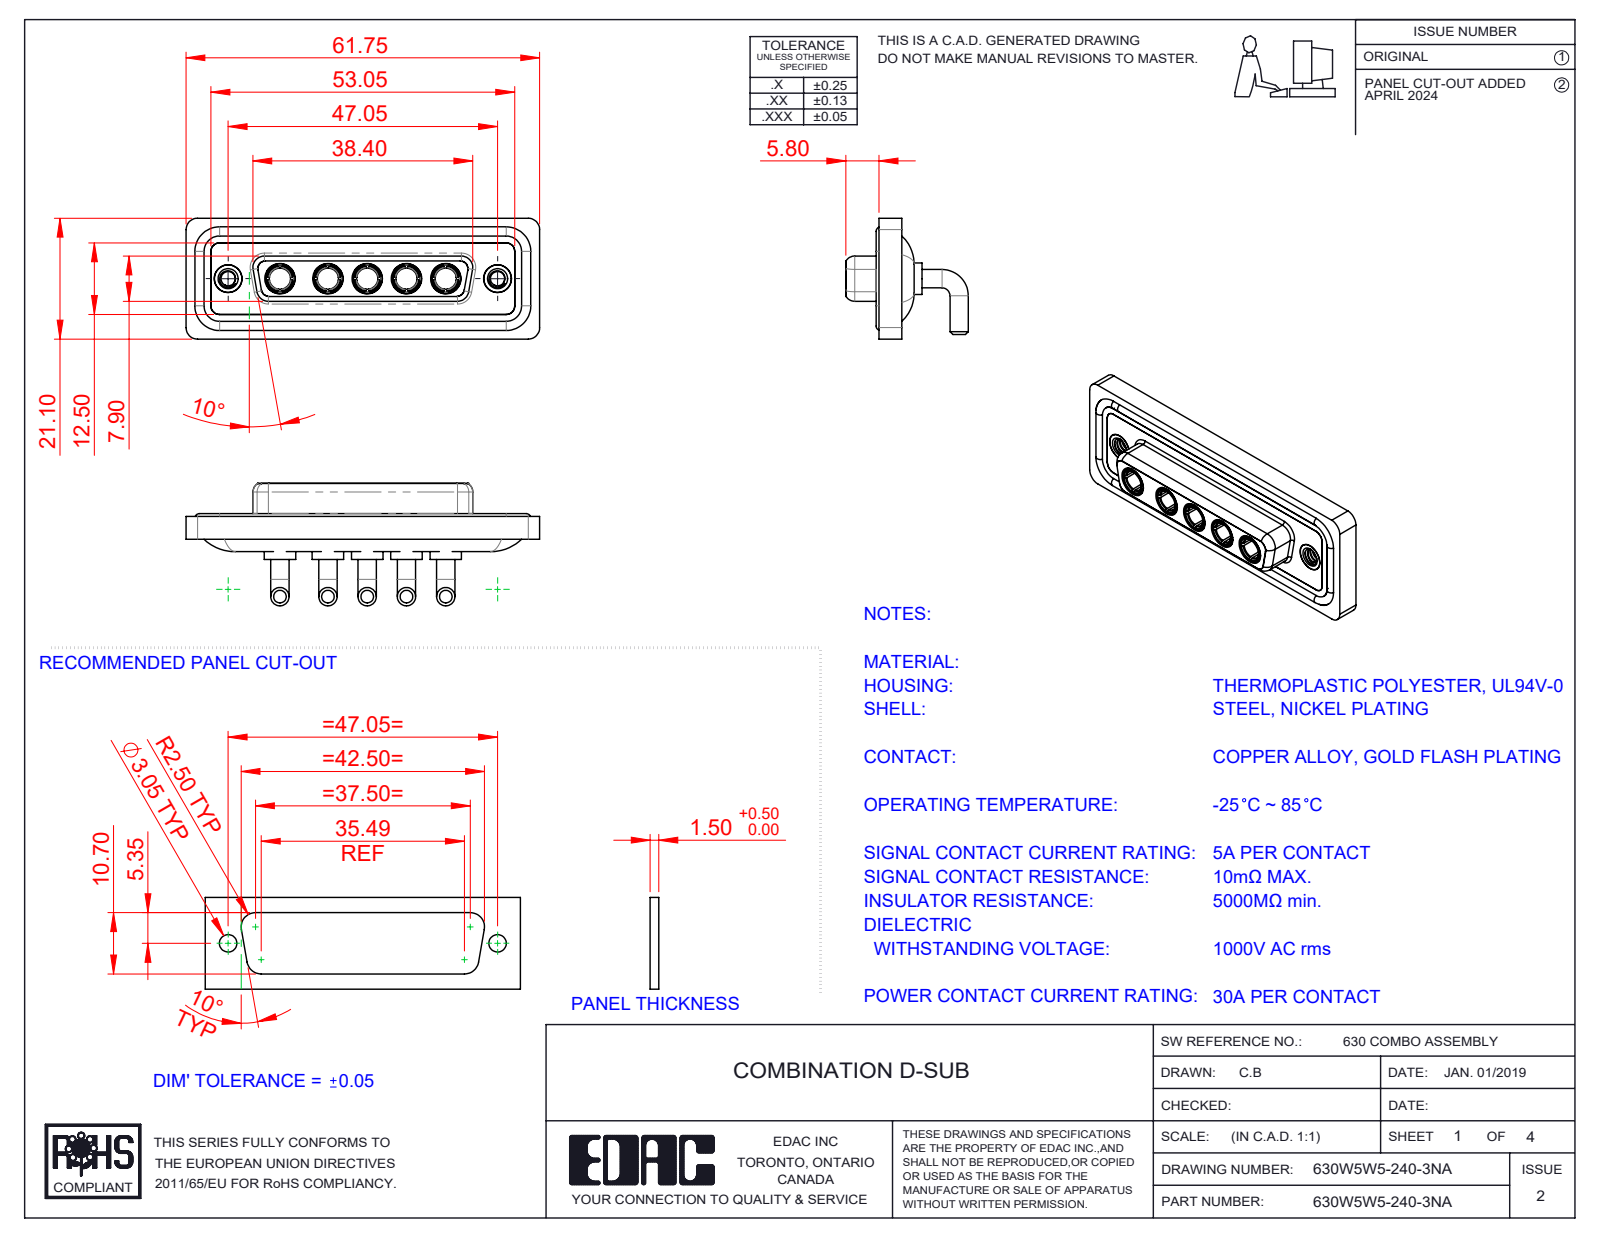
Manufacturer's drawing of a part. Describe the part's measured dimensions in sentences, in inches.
The part is named "630Combo Threaded Rivet_A; 630Combo Housing_5W5; 630Combo Waterproof Housing_25 Contacts; 630Combo Shell Front_25 Contacts (+3 more)". Its 3-D file was written by "SolidWorks 2023 (CONFIG_CONTROL_DESIGN)". It is 17 solids with 770 faces: 250 planar, 311 cylindrical and 209 other. Overall it measures 2.431 by 0.843 by 0.831 inches. Its volume is 0.523 cubic inches and its surface area 21.56 square inches. Round holes: 7 of diameter 0.191, 5 of diameter 0.146, 5 of diameter 0.209, 2 of diameter 0.098, 2 of diameter 0.157, 2 of diameter 0.159, 2 of diameter 0.197. Round bosses or shafts: 10 of diameter 0.126, 5 of diameter 0.217, 5 of diameter 0.205, 5 of diameter 0.195, 5 of diameter 0.187, 5 of diameter 0.148, 4 of diameter 0.063, 2 of diameter 0.195. Partial cylindrical surfaces (rounded edges, fillets, slot ends): 18 of radius 0.059, 18 of radius 0.079, 8 of radius 0.053, 8 of radius 0.063, 5 of radius 0.083, 4 of radius 0.01, 4 of radius 0.02, 4 of radius 0.024. The main face-to-face distances are 0.016, 0.071, 0.161, 0.043, 0.059, 0.098, 0.122, 0.146, 0.063, 0.114. The hole center spacings are 0.27, 0.356, 1.496, 0.27, 0.33, 0.54, 0.541, 0.6.
